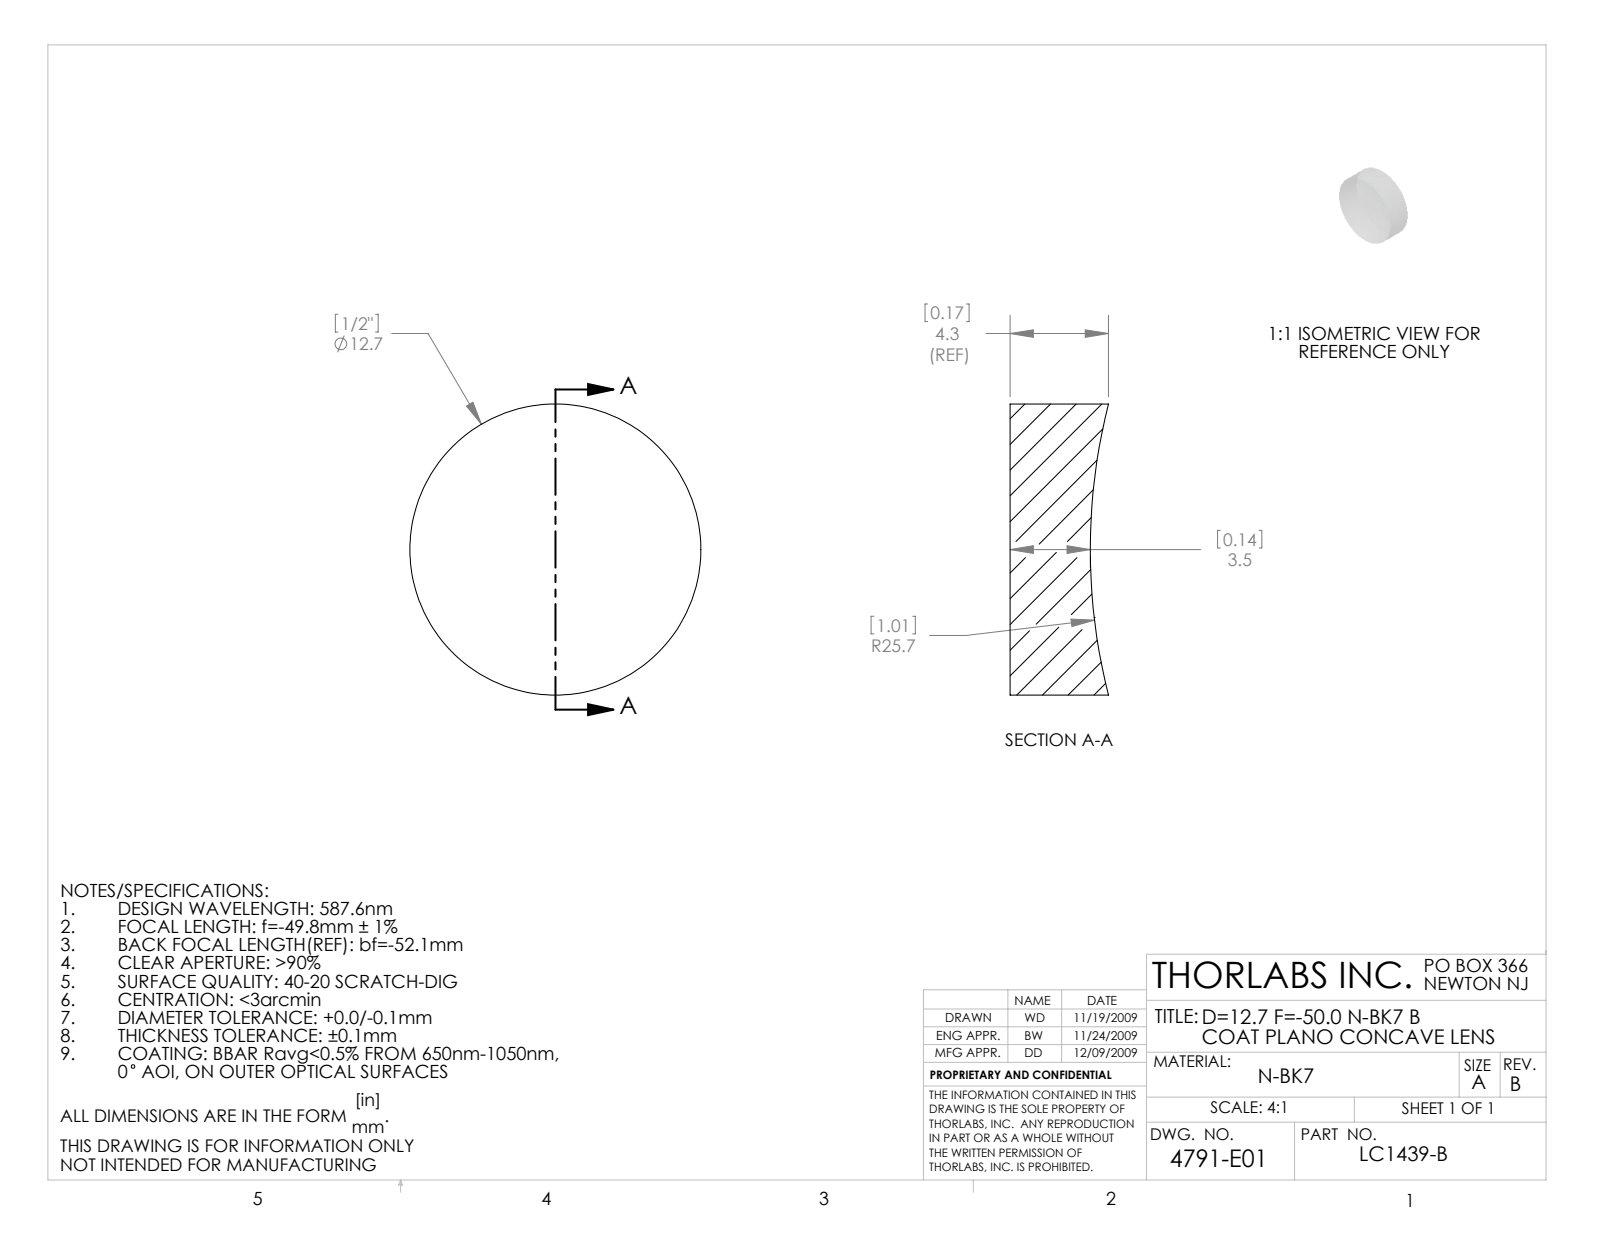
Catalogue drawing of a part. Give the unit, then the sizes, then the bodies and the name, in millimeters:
Units: millimetres
Overall size (bounding box): 12.7 × 12.7 × 4.3
Round bosses / shafts (diameter × count): ⌀12.7 ×1
Volume: 494 mm³ · Surface area: 427 mm²
Bodies: 1 solid, 5 faces (1 planar, 2 cylindrical, 2 other)
Part name (STEP PRODUCT): 4791-E0W
STEP written by: SolidWorks 2009 (AUTOMOTIVE_DESIGN)
